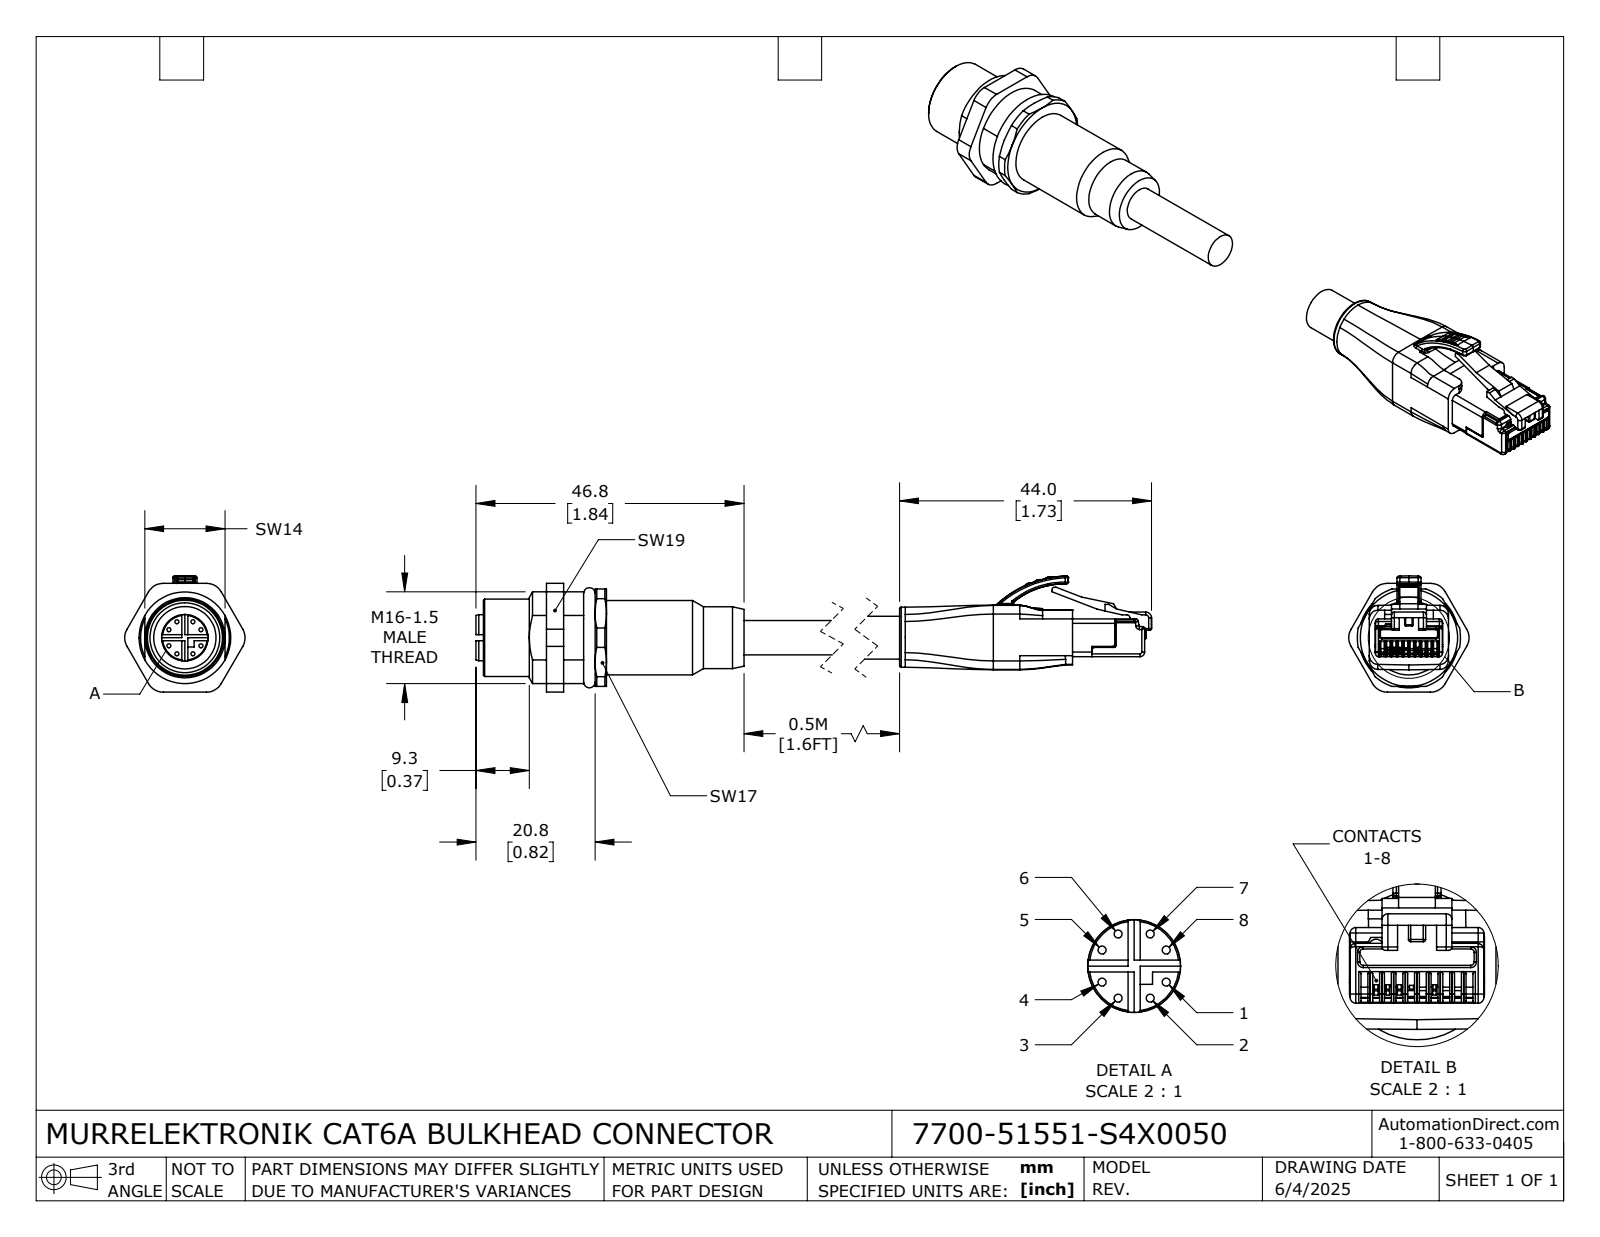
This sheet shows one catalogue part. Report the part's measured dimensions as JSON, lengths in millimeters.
{"part_name": "7700-51551-S4X0050_RJ45; 7700-51551-S4X0050_BULKHEAD; 7700-51551-S4X0050", "step_written_by": "SolidWorks 2024 (CONFIG_CONTROL_DESIGN)", "units": "millimeters", "bodies": {"solids": 3, "faces": 760, "planar": 351, "cylindrical": 231, "other": 178}, "overall_size": [143.8, 21.01, 20.29], "volume_mm3": 12565, "surface_area_mm2": 6720, "round_holes": [[0.7, 8], [10.9, 1], [12.2, 1], [16, 1]], "round_bosses_or_shafts": [[13.5, 1], [13, 1], [10.8, 1], [10.5, 1], [8.1, 1], [7.5, 1], [6, 1]], "partial_cylinders_radius": [[0.2, 61], [0.5, 25], [0.3, 14], [1.5, 9], [3, 6], [0.8, 5], [0.54, 2], [5, 2]], "face_to_face_distances": [13.9, 6.37, 1.06, 3, 14, 13.8, 10.5, 7.5, 8.5, 1], "hole_center_spacings": [3.13, 4.43, 1.98, 2.8, 5.6, 5.94, 6.26]}
